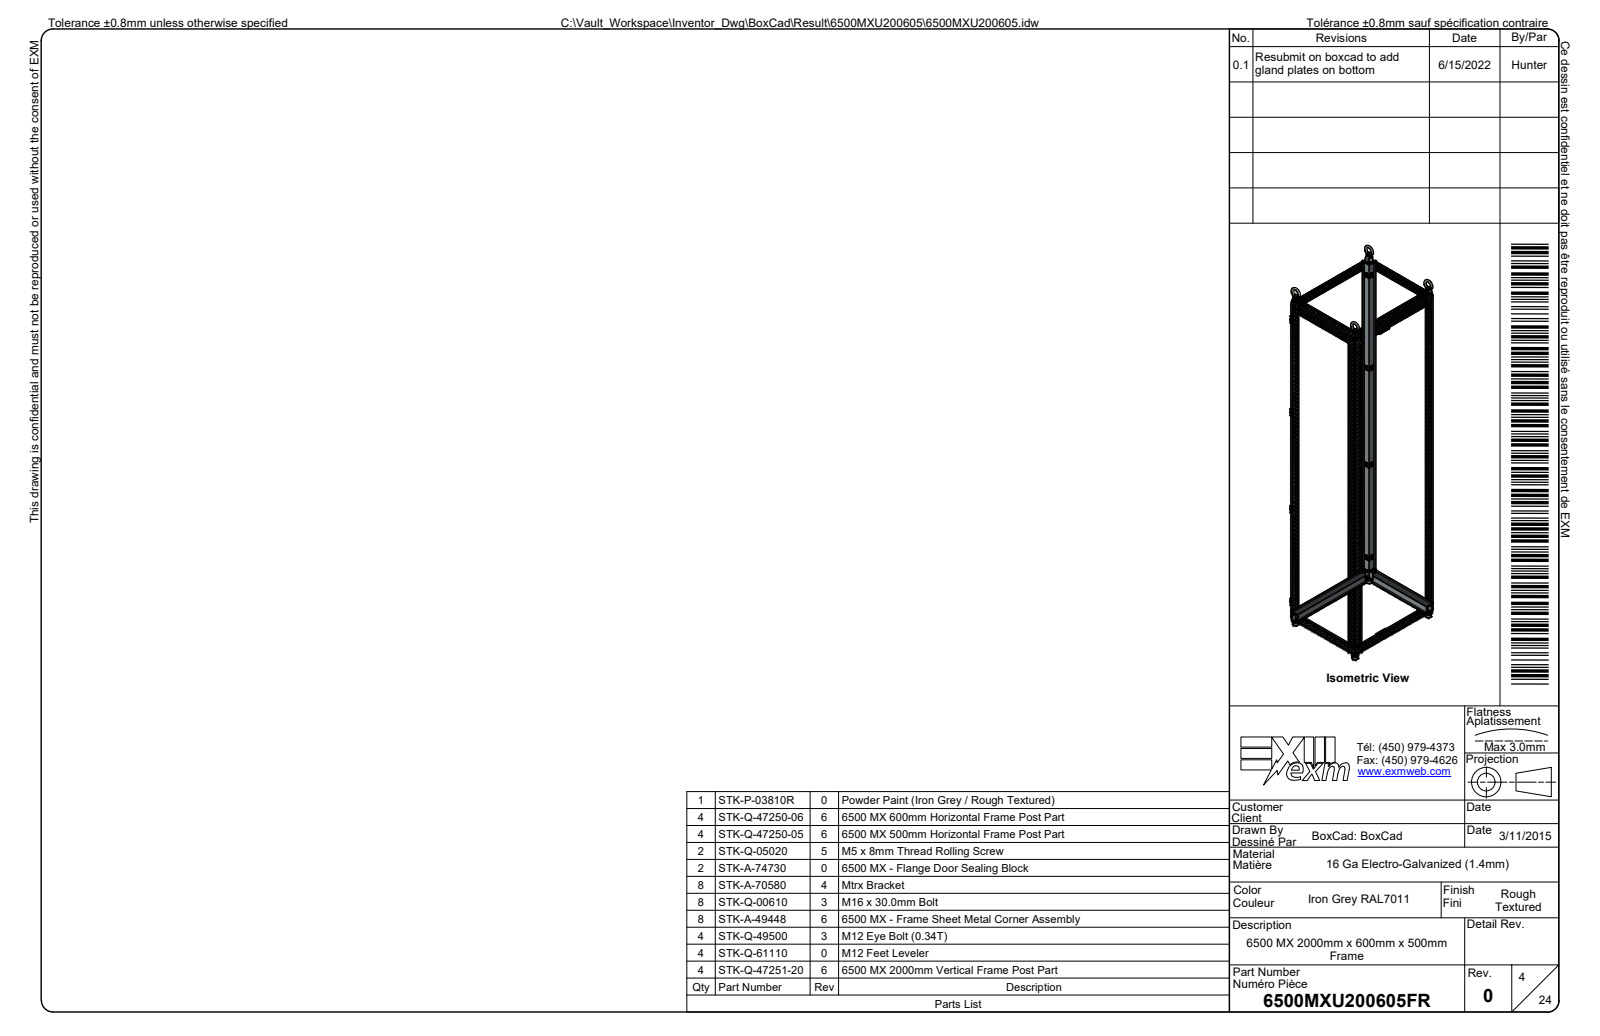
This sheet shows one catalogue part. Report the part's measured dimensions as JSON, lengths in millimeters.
{"part_name": "6500MXU200605; 6500MXU200605FR; 6500MXU200605CPOST-P; 6500MXU200605BPOST-P (+8 more)", "step_written_by": "Autodesk Inventor 2024 (AUTOMOTIVE_DESIGN)", "units": "millimeters", "bodies": {"solids": 325, "faces": 56700, "planar": 19813, "cylindrical": 17506, "other": 19381}, "overall_size": [2085, 610, 539], "volume_mm3": 16730000, "surface_area_mm2": 19460000, "round_holes": [[4.5, 1367], [4.2, 144], [0.8, 34], [4.9, 20], [5.1, 19], [1.1, 16], [5.2, 16], [5.8, 14], [5.5, 6], [6, 6], [9.5, 6], [5.1, 5]], "round_bosses_or_shafts": [[6, 144], [5.9, 62], [0.8, 34], [1, 24], [4.5, 20], [8.2, 16], [1, 12], [8.5, 11]], "partial_cylinders_radius": [[0.5, 1166], [1, 704], [0.1, 528], [0.3, 337], [0.3, 260], [3, 185], [0.8, 179], [2, 174]], "face_to_face_distances": [1.7, 508.3, 1.4, 608.6, 1.5, 55, 506.6, 53.3, 510, 455], "hole_center_spacings": [25, 50, 75, 100, 125, 150, 175, 18]}
